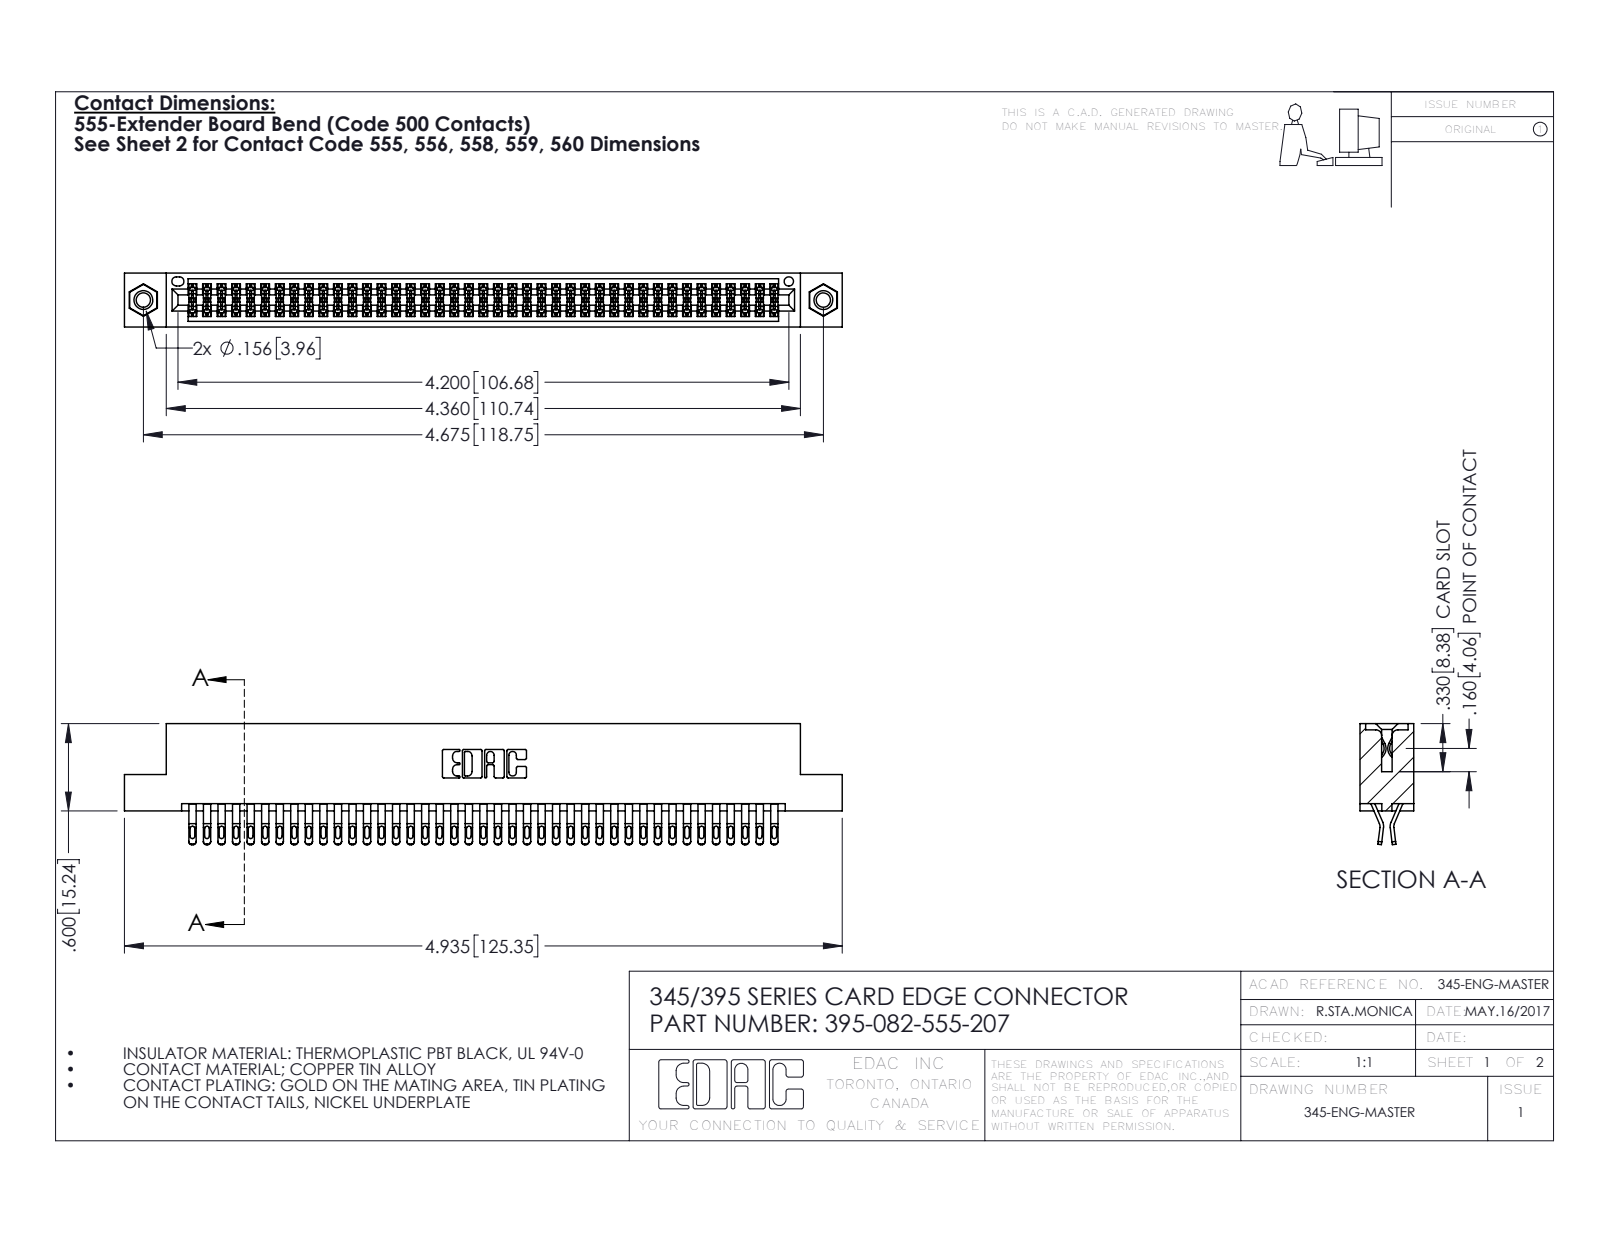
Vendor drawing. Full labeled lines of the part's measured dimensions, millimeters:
Part name (STEP PRODUCT): 345-292-001_555 Tail; 345-250-001_345-250-005-103; 345 Part_Flush Mounting Lugs - 0.156 Dia-TI; 395-082-555-207
STEP written by: SolidWorks 2016 (CONFIG_CONTROL_DESIGN)
Units: millimetres
Bodies: 85 solids, 4778 faces (2654 planar, 2108 cylindrical, 16 other)
Overall size (bounding box): 125.3 × 21.1 × 9.4
Volume: 12 400 mm³ · Surface area: 19 150 mm²
Round holes (diameter × count): ⌀2.5 ×2, ⌀3.2 ×2, ⌀4 ×2, ⌀1.6 ×1
Round bosses / shafts (diameter × count): ⌀3.9 ×2
Partial cylindrical surfaces — rounded edges, fillets, slot ends (radius × count): R0.4 ×205, R0.5 ×164, R0.2 ×123, R0.3 ×22, R0.2 ×6, R0.8 ×6, R0.7 ×3, R0.3 ×2
Main face-to-face distances: 1.8, 7.6, 0.6, 9.4, 5.1, 2.5, 6.9, 5.7, 4.4, 3.8
Hole centre spacings: 6.9, 112.8, 118.7
